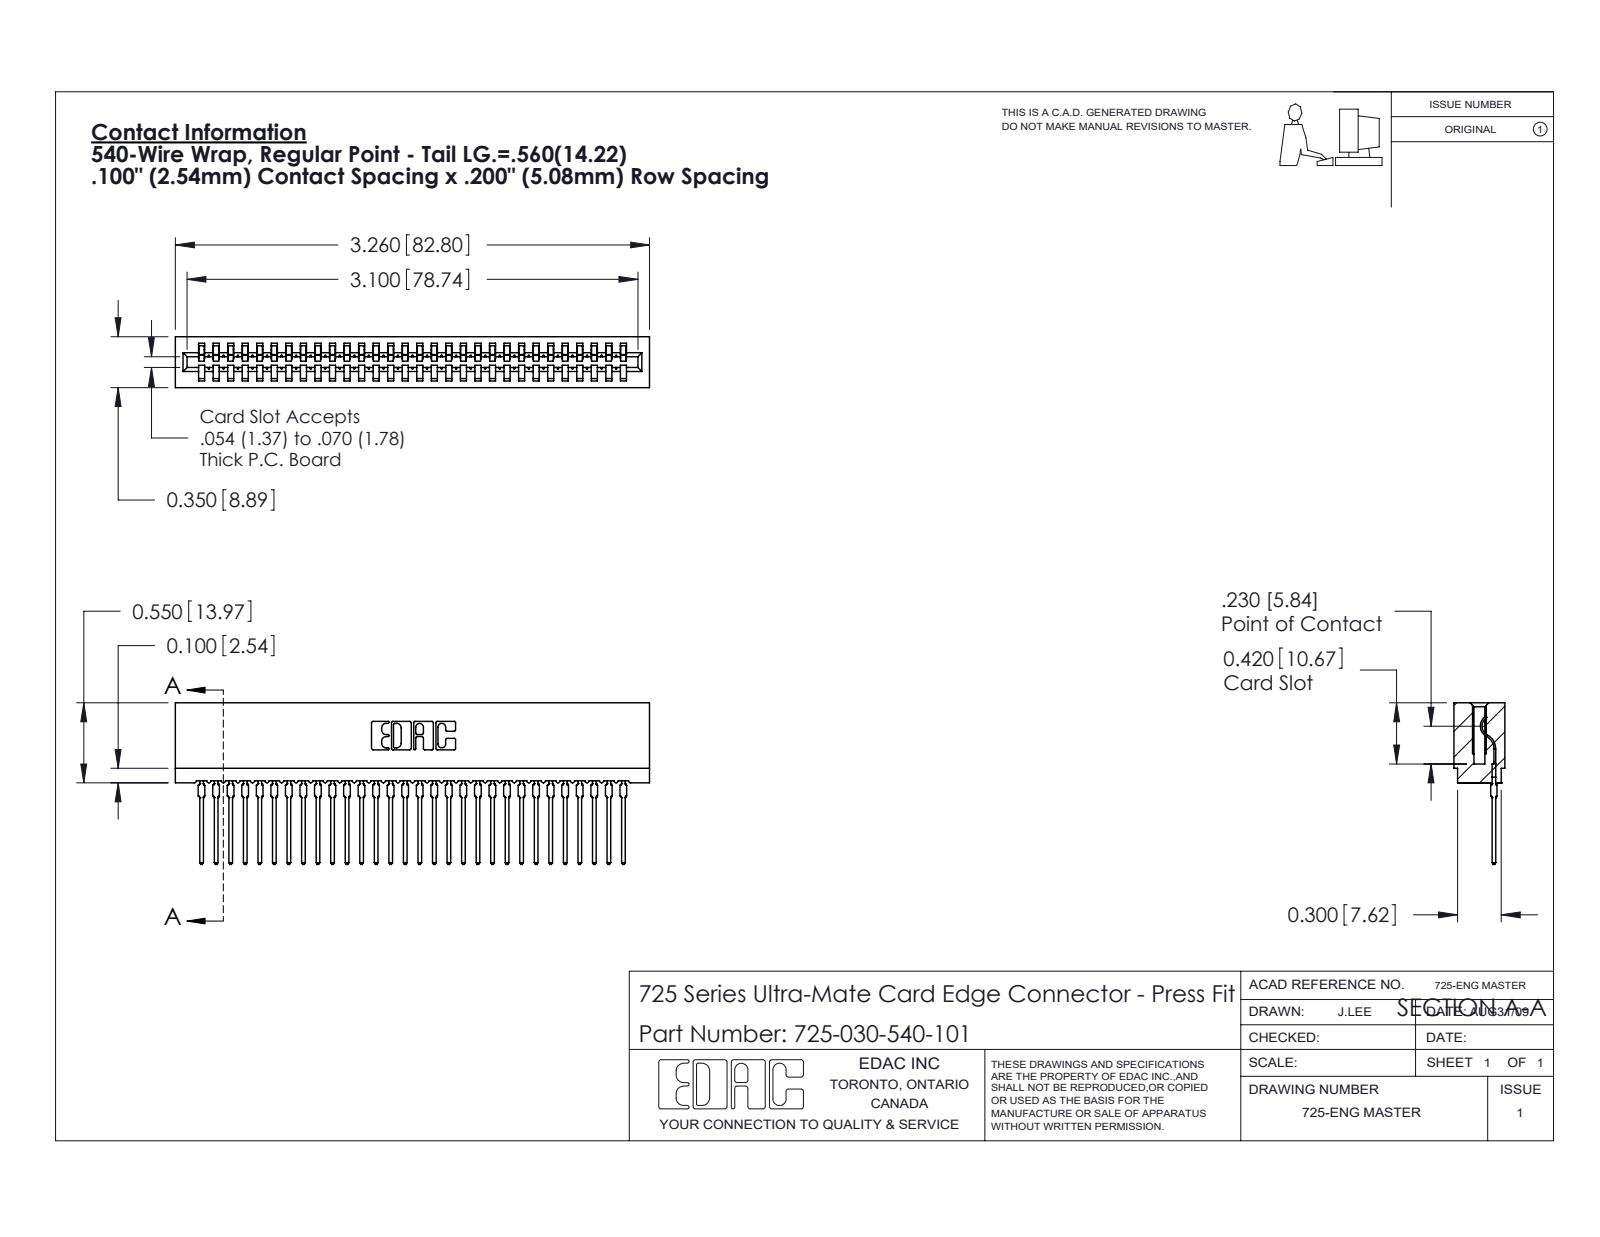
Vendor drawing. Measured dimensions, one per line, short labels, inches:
name: 745-292-001_540; 725-030-540-101; 725 Part_Insulator Option - 01
written by: SolidWorks 2020 (CONFIG_CONTROL_DESIGN)
unit: in
bodies: 31 solids, 3455 faces (2065 planar, 610 cylindrical, 780 other)
size: 3.26 × 1.111 × 0.35
volume: 0.392 in³; area: 19.33 in²
rounds: 60× R0.015, 60× R0.021, 22× R0.01, 6× R0.007, 6× R0.031, 4× R0.005, 4× R0.011, 3× R0.026
face distances: 0.2, 0.1, 0.35, 0.3, 0.4, 0.212, 0.138, 0.5, 0.063, 0.287
